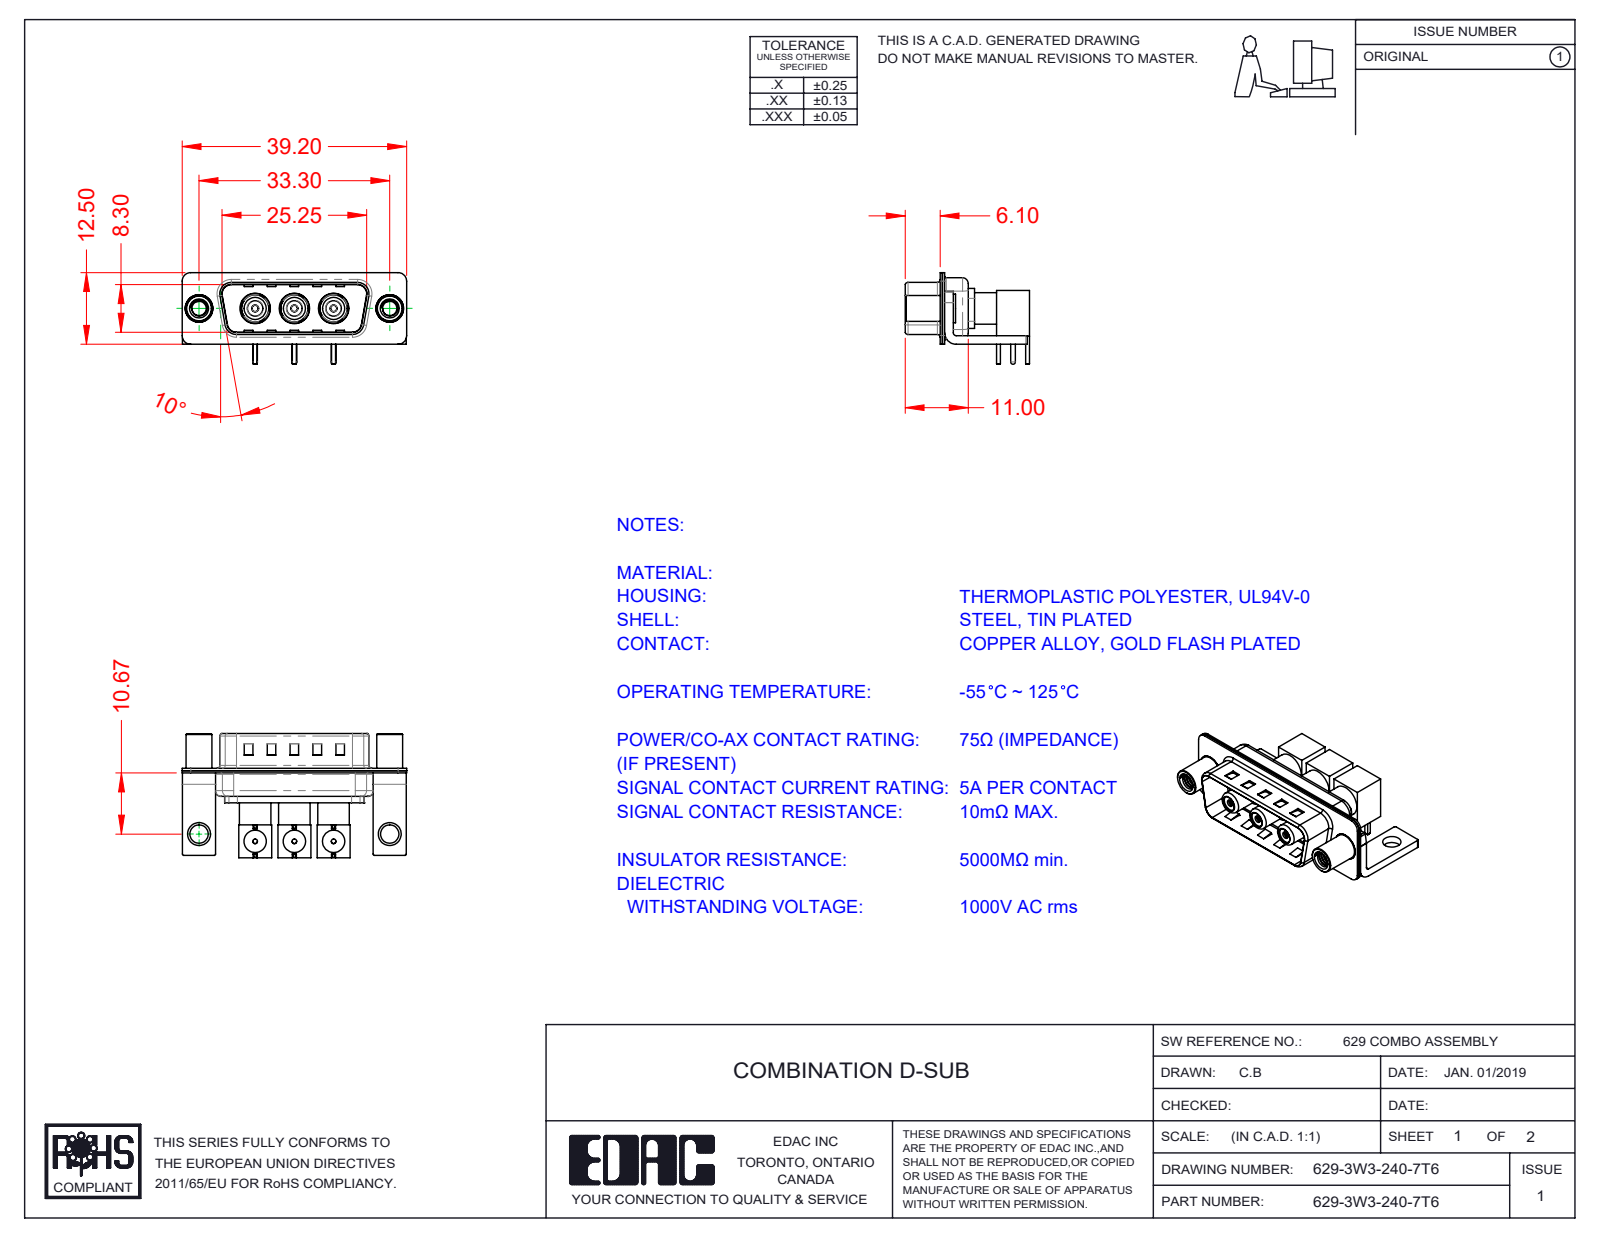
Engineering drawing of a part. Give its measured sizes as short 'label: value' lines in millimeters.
name: Insulator Socket 2; 629Combo Housing_3W3; Insulator Socket; Co-Ax Jack Assy_RA (+8 more)
written by: SolidWorks 2020 (CONFIG_CONTROL_DESIGN)
unit: mm
bodies: 28 solids, 894 faces (332 planar, 406 cylindrical, 156 other)
size: 39.2 × 21.71 × 16
volume: 3 081 mm³; area: 8 447 mm²
holes: 5× ⌀2.5, 3× ⌀0.8, 3× ⌀1.1, 3× ⌀1.2, 3× ⌀1.5, 3× ⌀1.6, 3× ⌀2.7, 3× ⌀3.1, 3× ⌀3.4, 3× ⌀3.9, 3× ⌀4.1, 3× ⌀4.85
bosses: 6× ⌀0.8, 3× ⌀5.5, 3× ⌀5.2, 3× ⌀4.8, 3× ⌀4.73, 3× ⌀4.16, 3× ⌀4, 3× ⌀3.85
rounds: 16× R0.25, 16× R1.5, 13× R2, 9× R0.5, 8× R1.6, 4× R0.6, 4× R0.65, 4× R0.9
face distances: 0.4, 0.8, 1.5, 5.75, 9.5, 1.4, 9.1, 8.7, 1.1, 0.35
hole spacings: 6.85, 13.7, 9.88, 16.7, 23.53, 9.8, 16.65, 23.5
